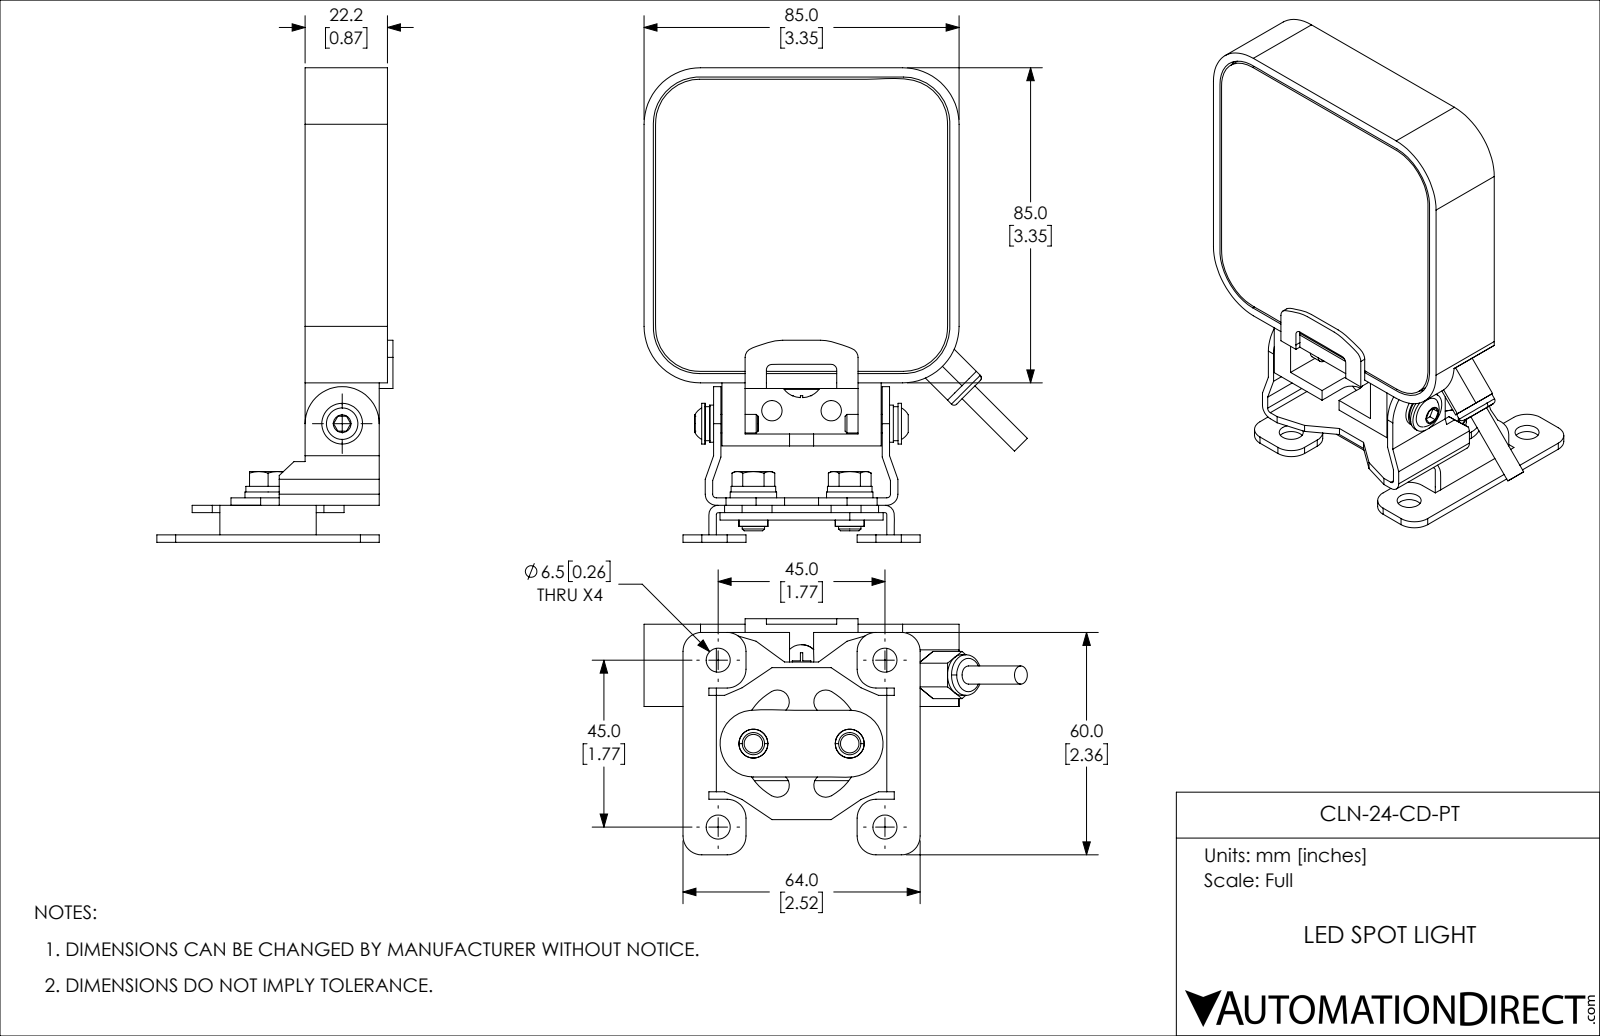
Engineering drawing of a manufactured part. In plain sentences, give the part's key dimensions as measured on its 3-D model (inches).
The part is named "CLN-24-CD-PT". Its 3-D file was written by "SolidWorks 2018 (AUTOMOTIVE_DESIGN)". It is 9 solids with 359 faces: 183 planar, 101 cylindrical and 75 other. Overall it measures 5.039 by 4.072 by 2.508 inches. Its volume is 8.846 cubic inches and its surface area 79.91 square inches. Round holes: 4 of diameter 0.256, 3 of diameter 0.236, 3 of diameter 0.252, 2 of diameter 0.217, 1 of diameter 0.197, 1 of diameter 0.213. Round bosses or shafts: 2 of diameter 0.492, 2 of diameter 0.472, 2 of diameter 0.433, 2 of diameter 0.307, 1 of diameter 0.394, 1 of diameter 0.37, 1 of diameter 0.362, 1 of diameter 0.193. Partial cylindrical surfaces (rounded edges, fillets, slot ends): 12 of radius 0.2, 4 of radius 0.6, 2 of radius 0.039, 2 of radius 0.118, 2 of radius 0.315, 1 of radius 0.394, 1 of radius 0.638. The main face-to-face distances are 0.079, 0.697, 0.394, 0.315, 0.157, 0.236, 0.177, 0.874, 0.335, 3.346. The hole center spacings are 0.961, 1.253, 1.655, 1.772, 0.512, 2.506, 0.63, 1.024.
